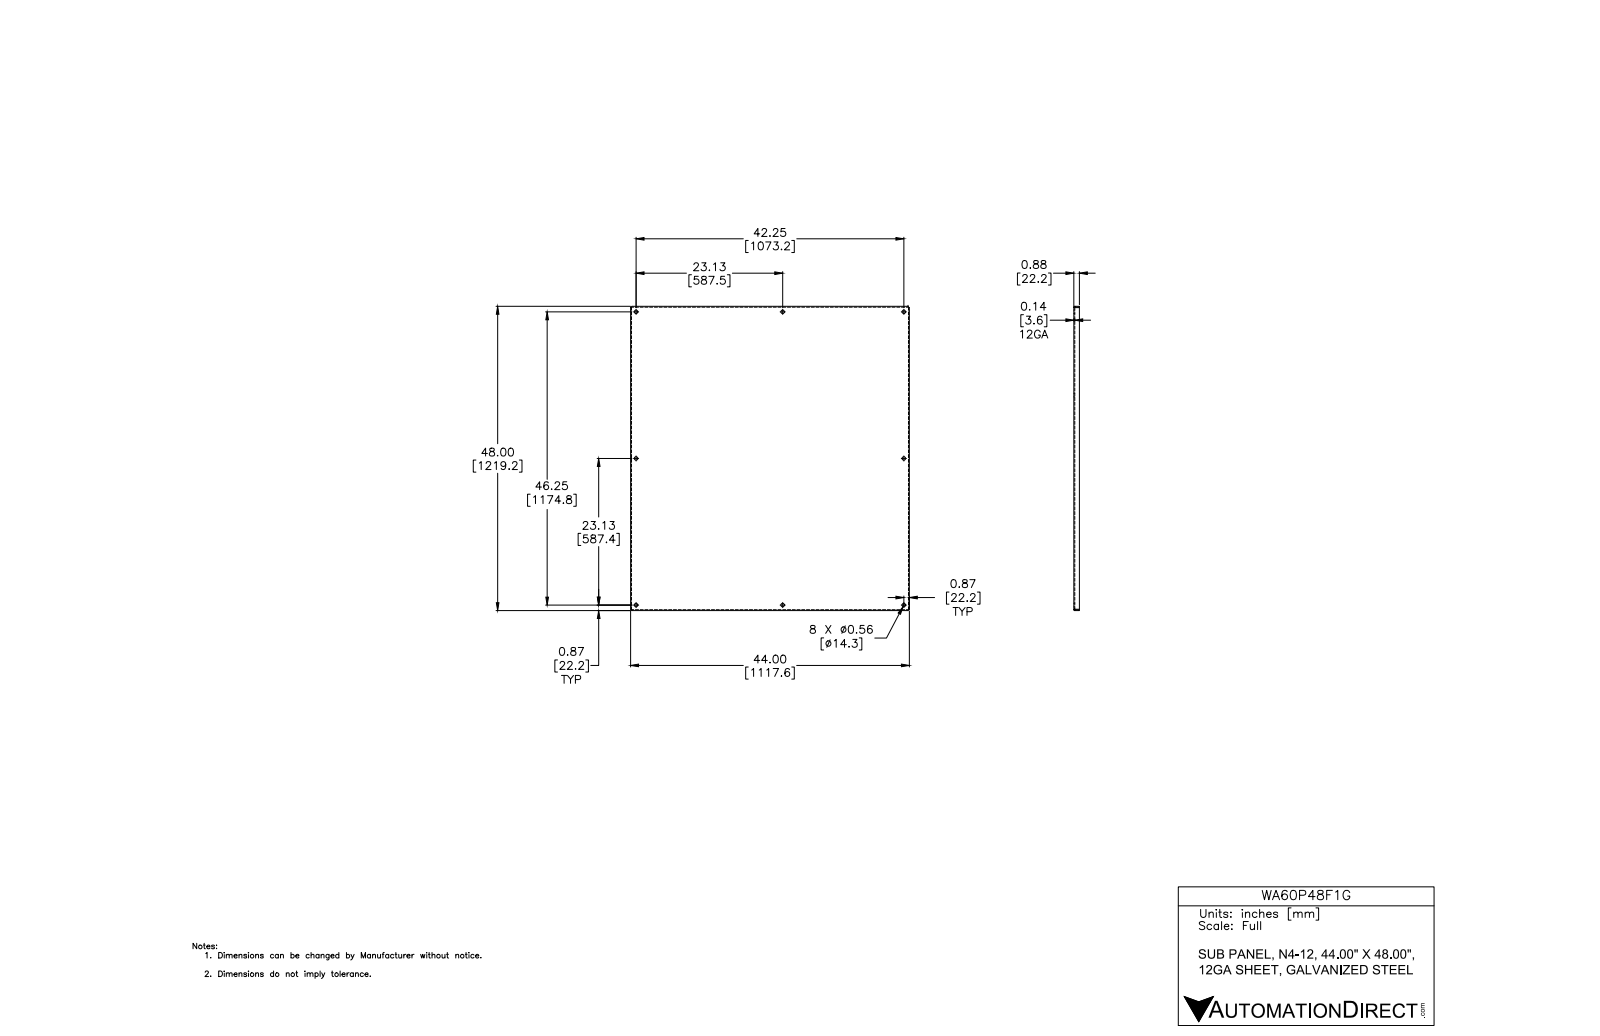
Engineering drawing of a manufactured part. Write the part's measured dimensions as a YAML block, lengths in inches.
part_name: "WA_P_F_G"
step_written_by: "Autodesk Inventor 2012 (AUTOMOTIVE_DESIGN)"
units: inches
bodies: {solids: 1, faces: 46, planar: 22, cylindrical: 16, other: 8}
overall_size: [48, 44, 0.875]
volume: 280.1
surface_area: 4506
round_holes:
  - {diameter: 0.563, count: 8}
partial_cylinders:
  - {radius: 0.016, count: 4}
  - {radius: 0.141, count: 4}
face_to_face_distances: [0.125, 47.875, 0.125, 43.875, 43.75, 44, 43.875, 48, 47.75, 0.75]
hole_center_spacings: [23.125, 21.125, 21.125, 31.321, 31.322, 42.25, 46.25, 48.165]
